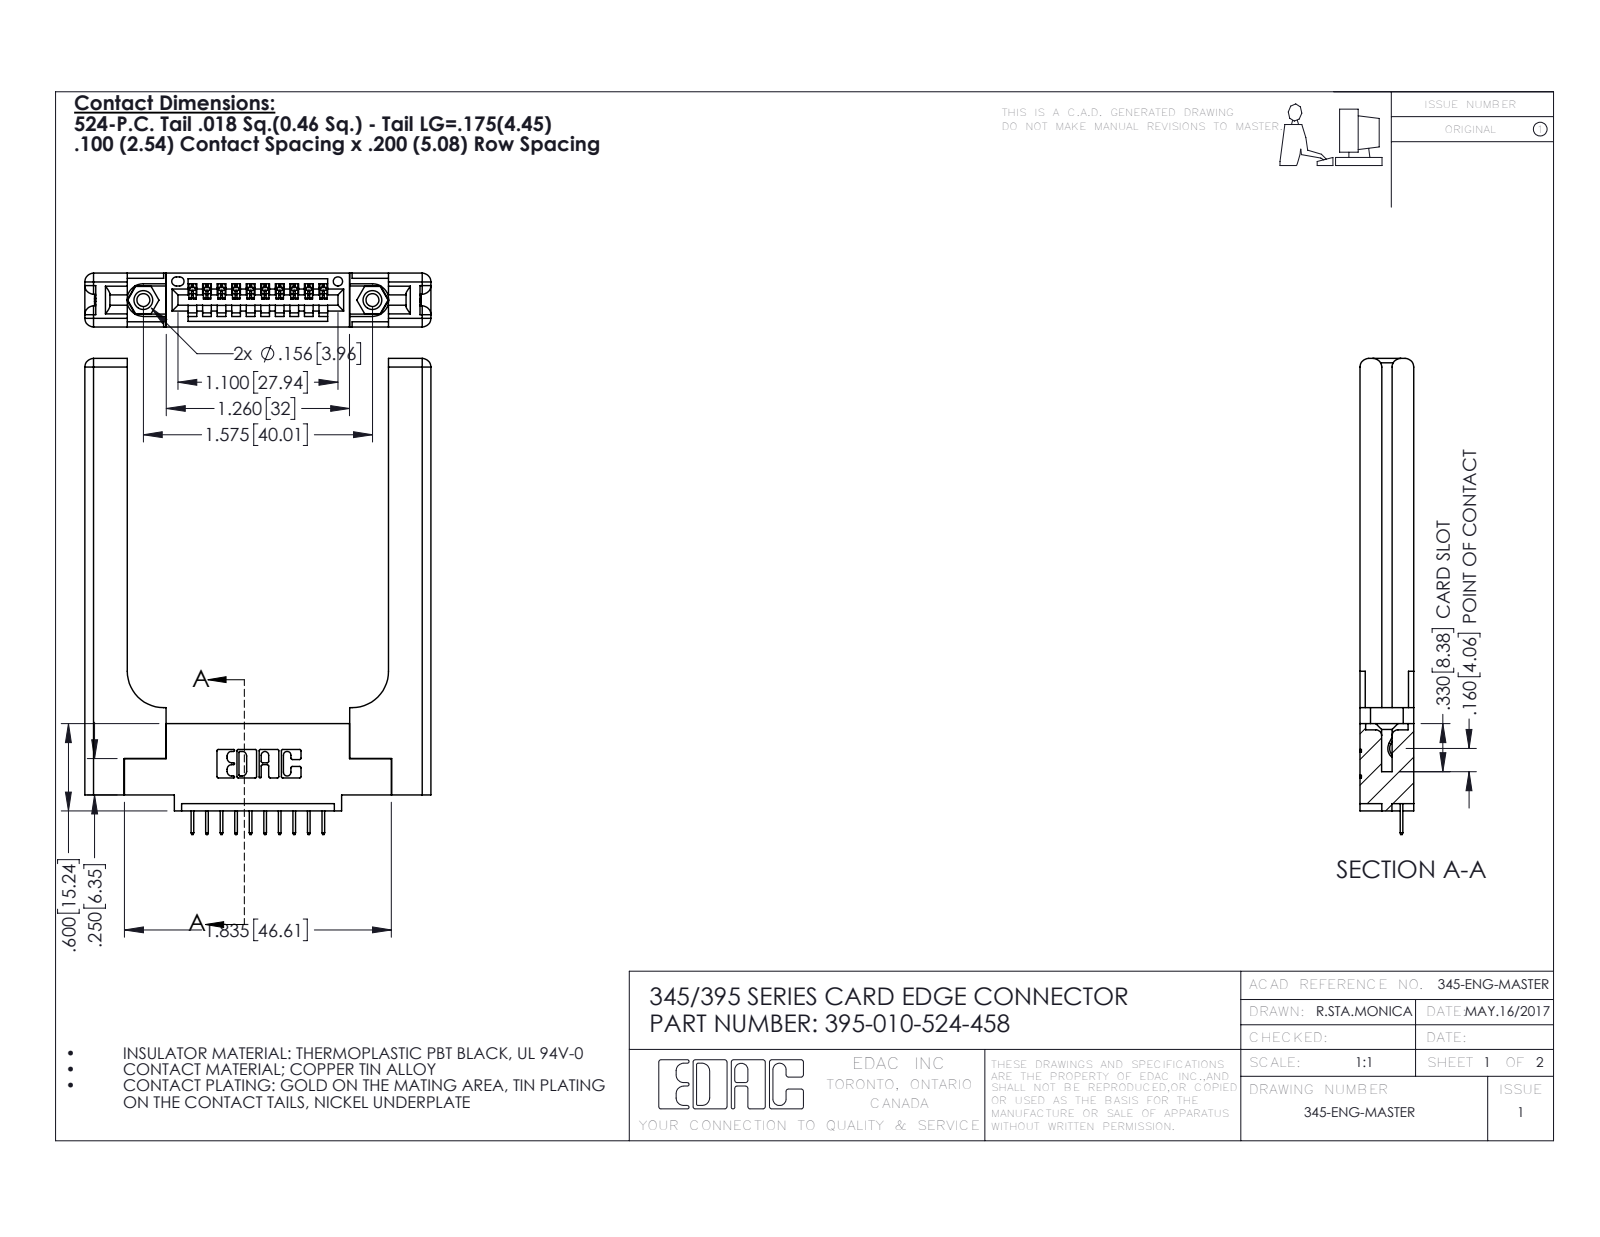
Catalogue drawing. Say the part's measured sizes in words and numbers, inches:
The part is named "345 Part_0.110 Offset - 0.156 Dia-TH; 345-292-001_345-293-124; 345-220-058_345-220-058; 345-250-001_345-250-001-102 (+1 more)". Its 3-D file was written by "SolidWorks 2016 (CONFIG_CONTROL_DESIGN)". It is 15 solids with 1006 faces: 692 planar, 254 cylindrical and 60 other. Overall it measures 3.272 by 2.379 by 0.37 inches. Its volume is 0.846 cubic inches and its surface area 18.53 square inches. Round holes: 2 of diameter 0.089, 2 of diameter 0.125, 2 of diameter 0.156, 1 of diameter 0.064. Round bosses or shafts: 2 of diameter 0.155. Partial cylindrical surfaces (rounded edges, fillets, slot ends): 22 of radius 0.01, 20 of radius 0.006, 16 of radius 0.06, 6 of radius 0.007, 6 of radius 0.031, 3 of radius 0.026, 2 of radius 0.03, 2 of radius 0.031. The main face-to-face distances are 0.37, 0.15, 0.22, 0.072, 0.148, 0.077, 0.298, 1.796, 0.071, 0.292. The hole center spacings are 0.27, 1.344, 1.575.
